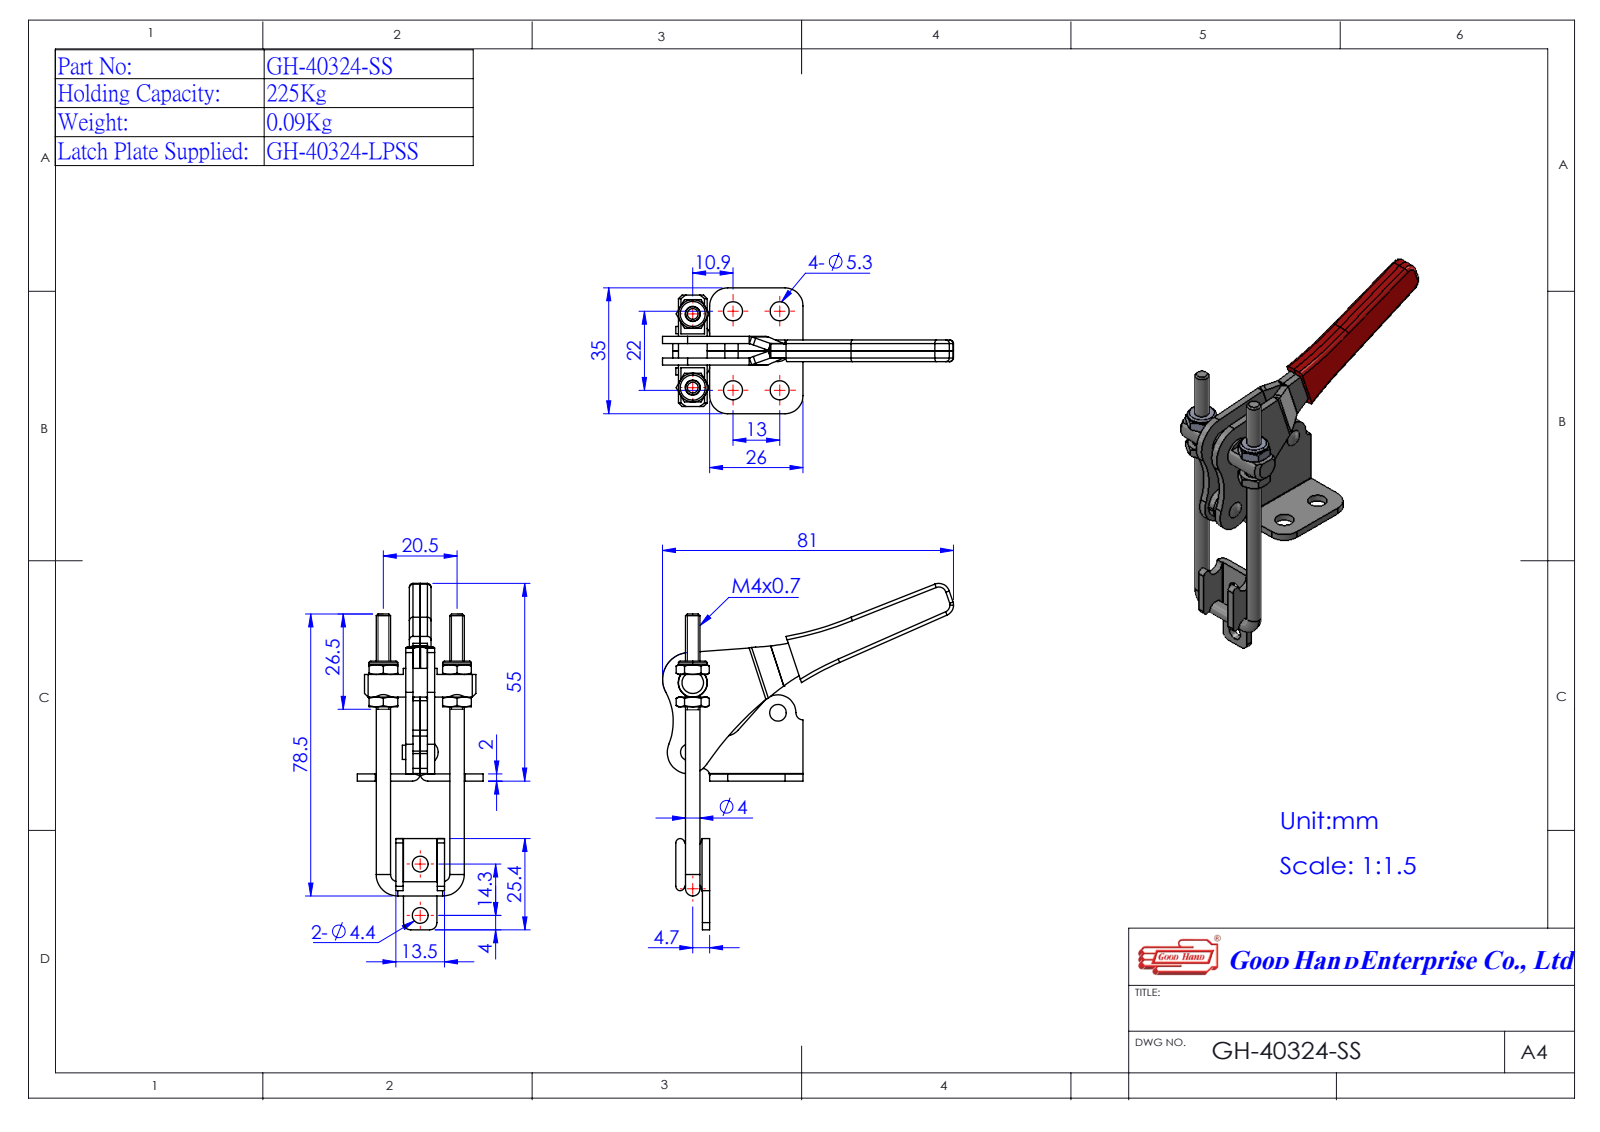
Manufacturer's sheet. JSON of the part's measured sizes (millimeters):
{"part_name": "44032444-1^GH-40324-SS(簡化); 14032414-1^GH-40324-SS(簡化); Group1^GH-40324-SS(簡化); Group2^GH-40324-SS(簡化) (+2 more)", "step_written_by": "SolidWorks 2016 (AUTOMOTIVE_DESIGN)", "units": "millimeters", "bodies": {"solids": 7, "faces": 345, "planar": 126, "cylindrical": 133, "other": 86}, "overall_size": [96.4, 81, 35], "volume_mm3": 14238, "surface_area_mm2": 13409, "round_holes": [[5.3, 4], [3.05, 2], [4.2, 2], [4.4, 2], [4.5, 2], [5, 2], [8, 1]], "round_bosses_or_shafts": [[4, 5], [8, 2]], "partial_cylinders_radius": [[0.1, 8], [2.1, 8], [5, 6], [85.33, 3], [89.5, 3], [1.2, 2], [2.5, 2], [3, 2]], "face_to_face_distances": [2, 1, 6, 4, 7, 5, 8, 8.75, 2.75, 10.75], "hole_center_spacings": [11.23, 13, 22, 24.02, 24.21, 25.55, 32.21, 14.3]}
